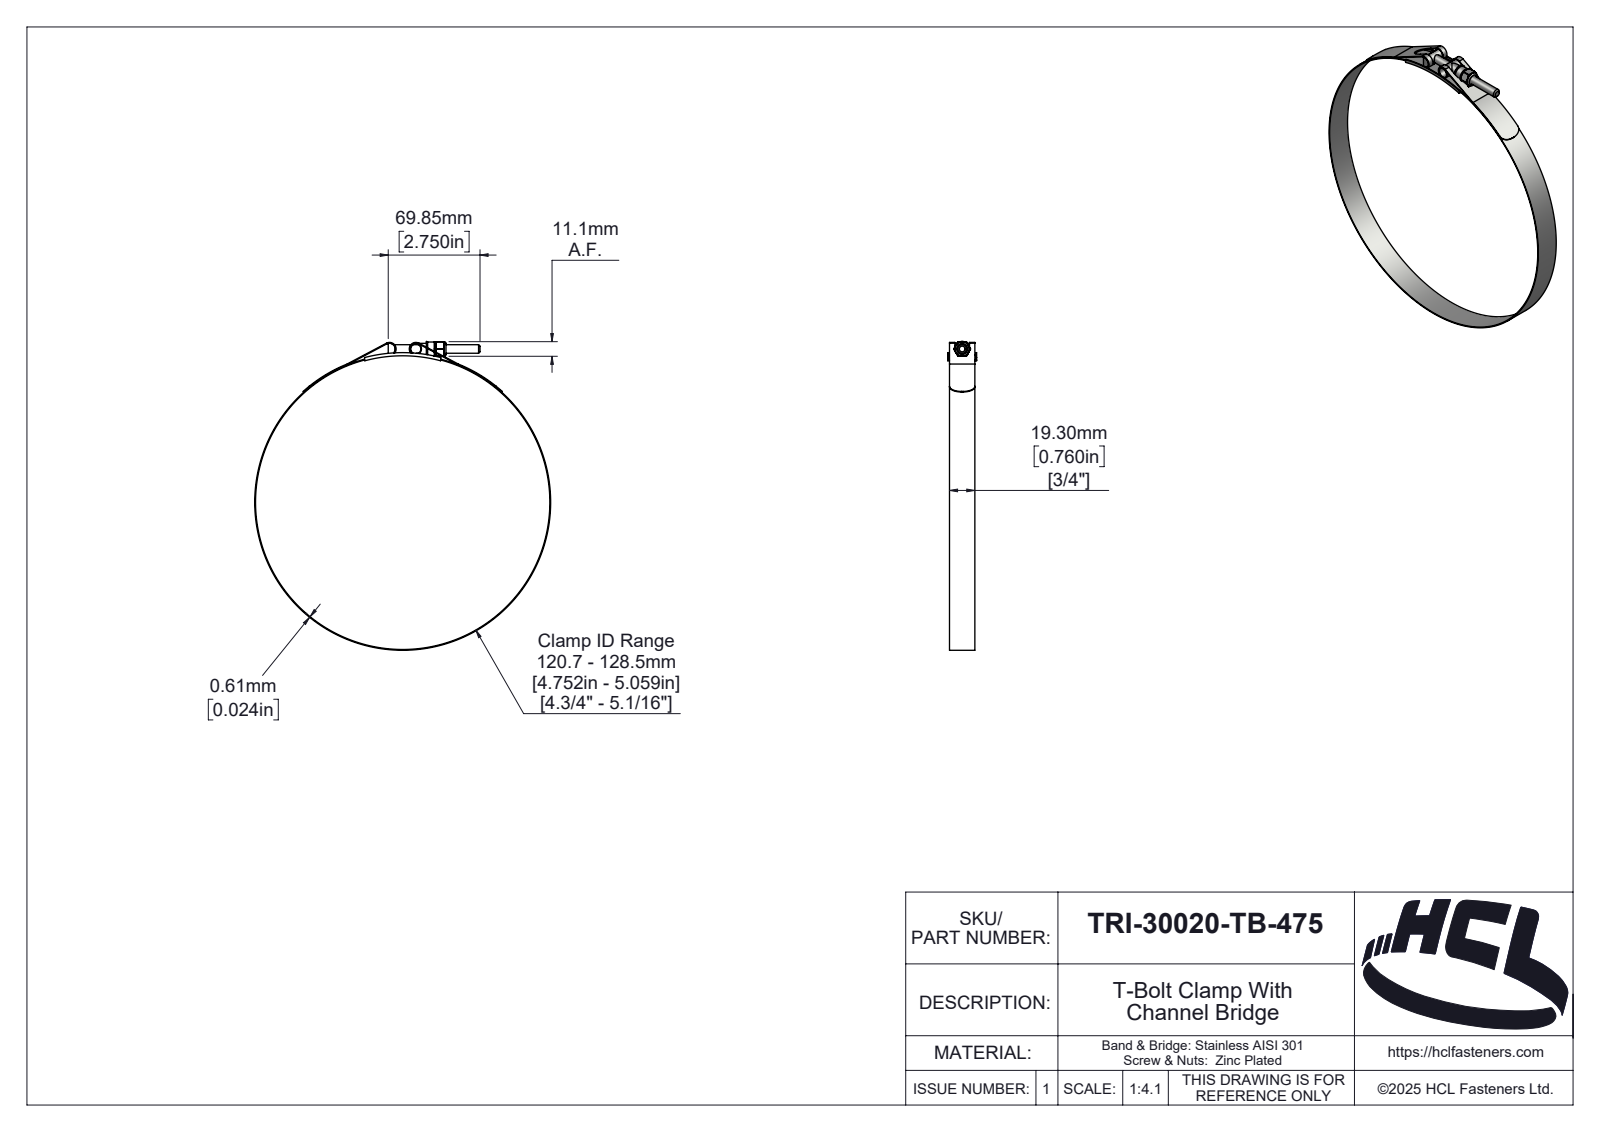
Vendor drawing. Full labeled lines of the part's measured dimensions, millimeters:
Part name (STEP PRODUCT): TRI-30020-TB-475
STEP written by: SolidWorks 2025 (AUTOMOTIVE_DESIGN)
Units: millimetres
Bodies: 6 solids, 330 faces (44 planar, 122 cylindrical, 164 other)
Overall size (bounding box): 234.9 × 225.22 × 22
Volume: 14 858 mm³ · Surface area: 40 604 mm²
Round holes (diameter × count): ⌀5.4 ×1, ⌀6.35 ×1, ⌀6.5 ×1, ⌀7.58 ×1, ⌀224 ×1
Round bosses / shafts (diameter × count): ⌀8.58 ×2, ⌀225.22 ×1, ⌀10.58 ×1
Partial cylindrical surfaces — rounded edges, fillets, slot ends (radius × count): R0.39 ×6, R0.5 ×2, R4.39 ×2, R5 ×2, R0.59 ×1, R2.42 ×1, R3.03 ×1, R3.19 ×1
Main face-to-face distances: 0.61, 19.3, 1.35, 20.65, 0.74, 21.39, 20.04, 22, 11.11, 20.78
Hole centre spacings: 117
